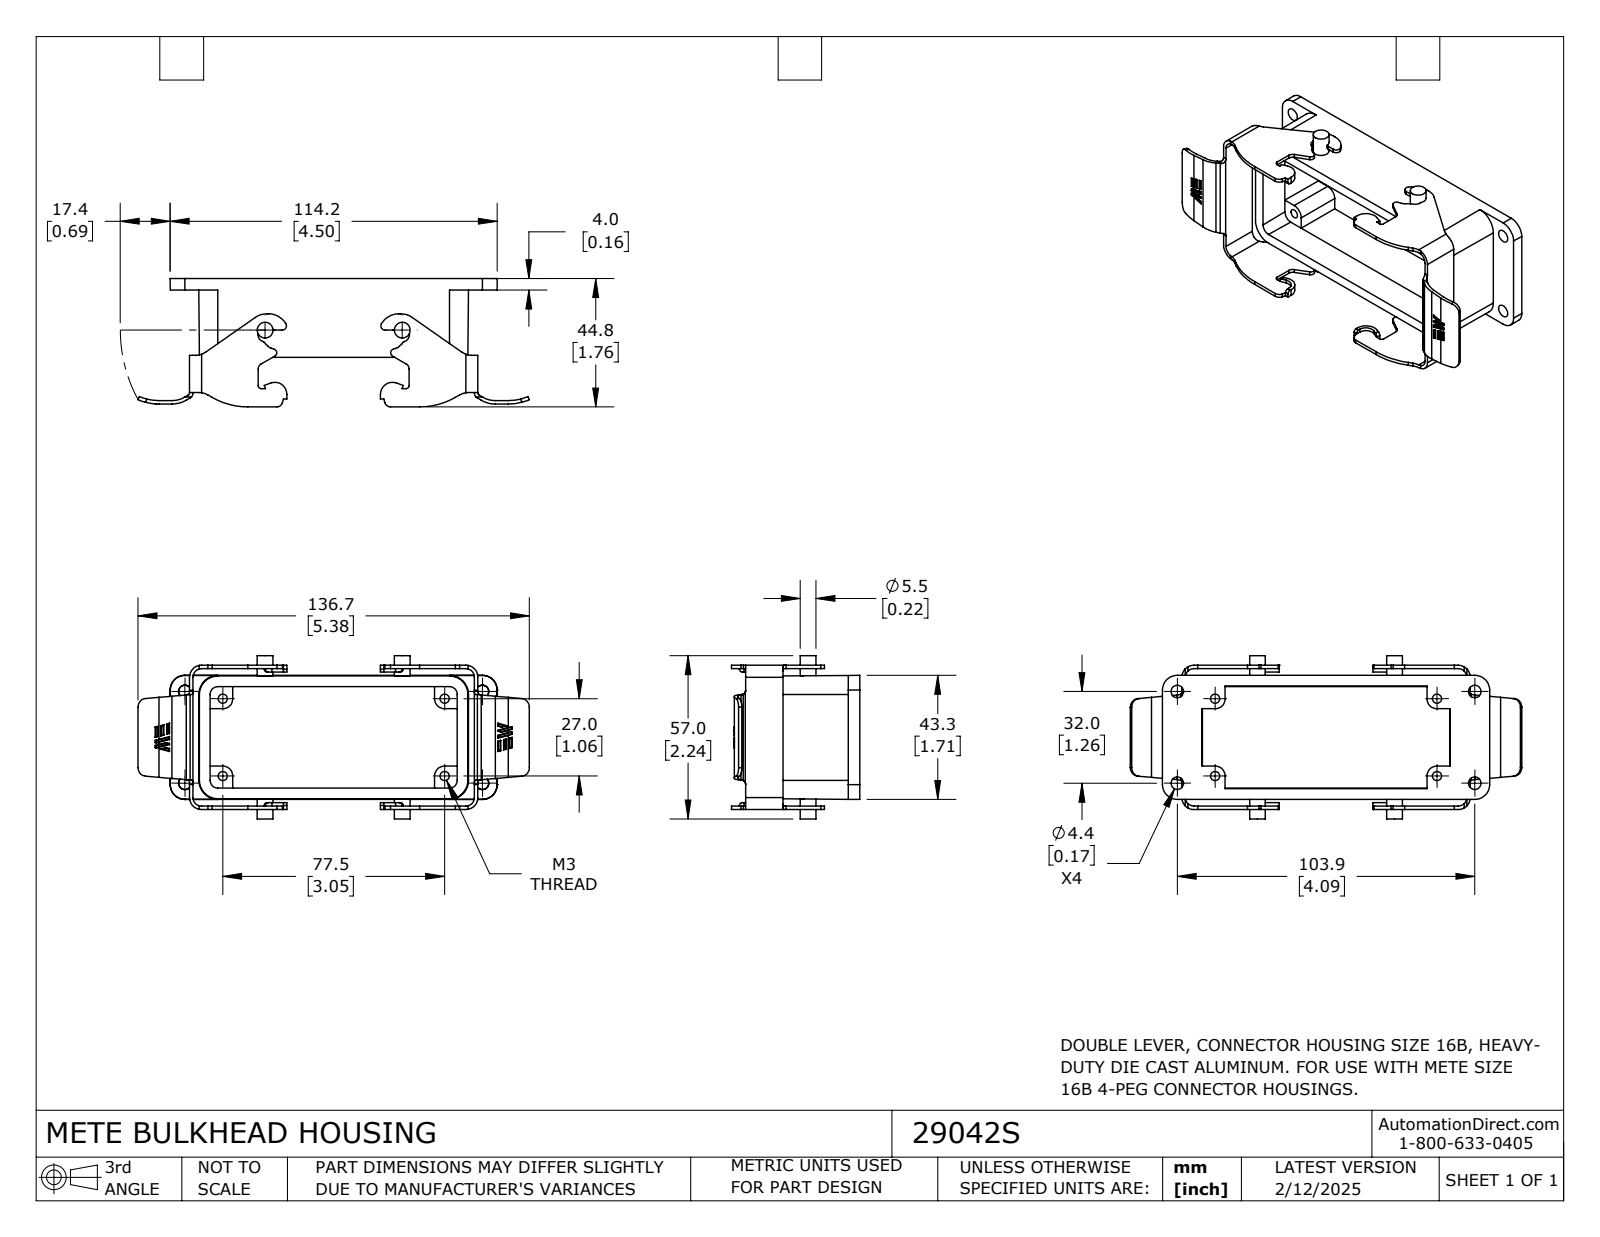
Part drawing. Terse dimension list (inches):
name: 29042S
written by: SolidWorks 2024 (CONFIG_CONTROL_DESIGN)
unit: in
bodies: 1 solid, 362 faces (162 planar, 172 cylindrical, 28 other)
size: 5.382 × 2.244 × 1.764
volume: 2.371 in³; area: 46.78 in²
holes: 4× ⌀0.126
bosses: 2× ⌀0.217
rounds: 32× R0.008, 10× R0.039, 10× R0.118, 6× R0.059, 6× R0.079, 6× R0.165, 4× R0.098, 4× R0.138
face distances: 0.047, 1.937, 0.287, 1.697, 0.24, 1.65, 1.89, 1.984, 1.409, 3.917
hole spacings: 1.063, 3.051, 3.231
